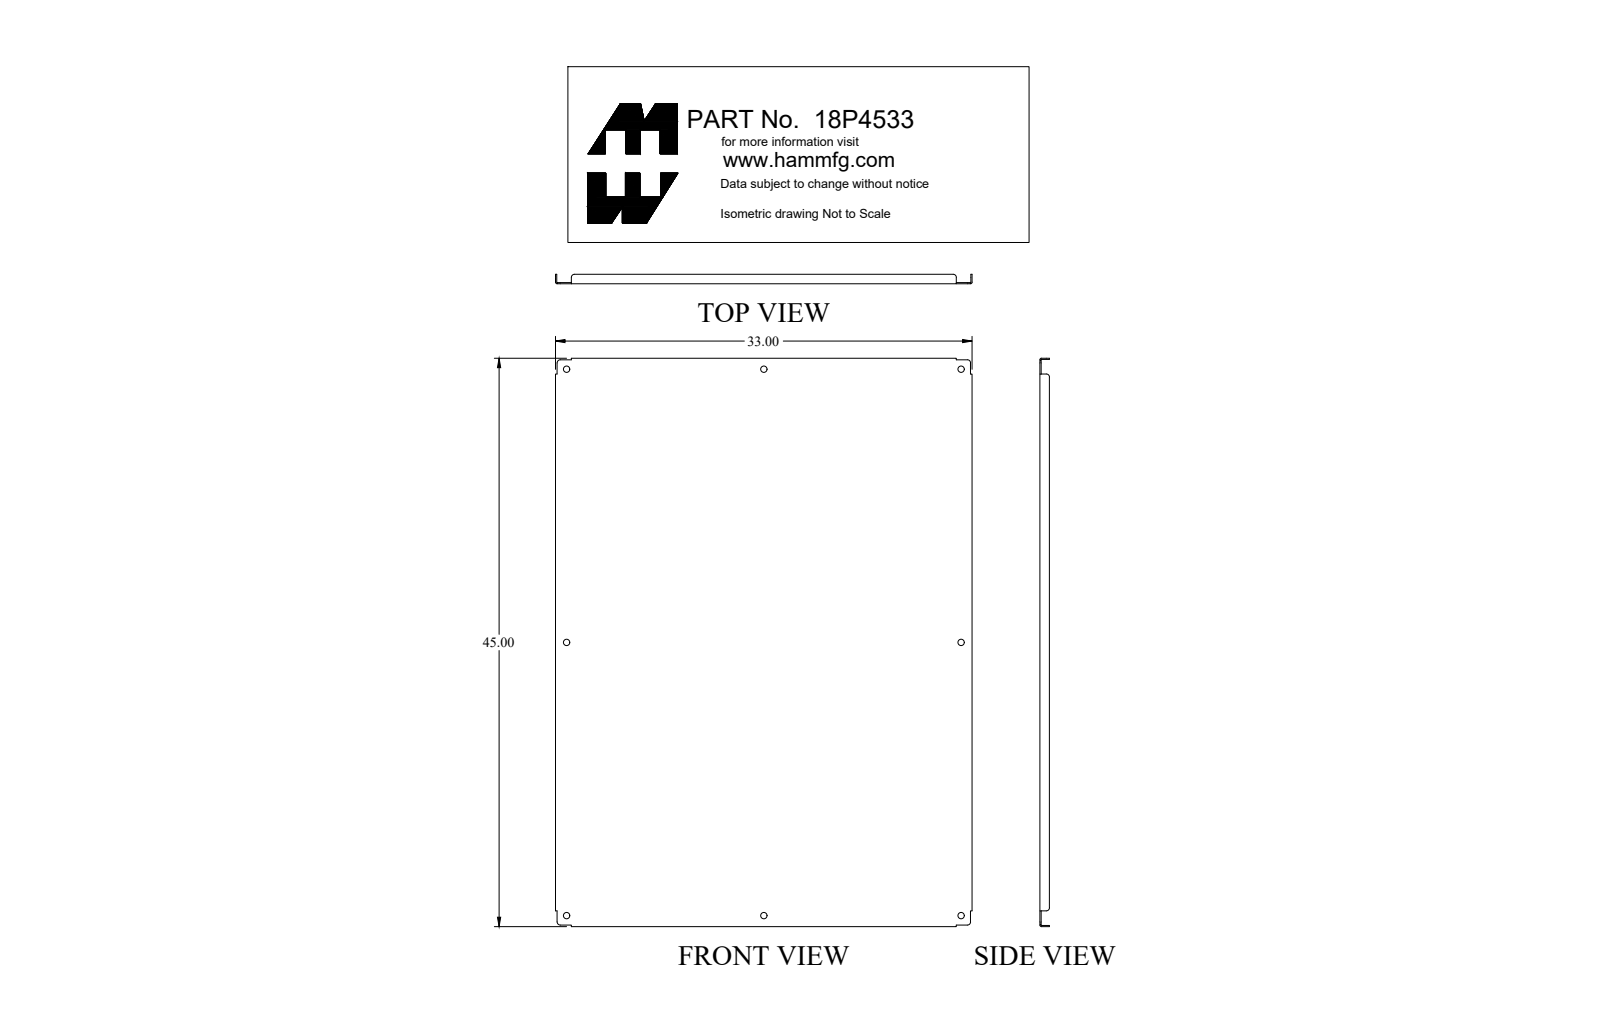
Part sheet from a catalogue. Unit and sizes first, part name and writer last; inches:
Units: inches
Overall size (bounding box): 45 × 33 × 0.75
Round holes (diameter × count): ⌀0.5 ×8
Partial cylindrical surfaces — rounded edges, fillets, slot ends (radius × count): R0.25 ×8, R0.03 ×4, R0.125 ×4
Main face-to-face distances: 0.095, 32.905, 44.905, 32.81, 33, 45, 44.81, 0.75, 0.655, 0.125
Hole centre spacings: 15.625, 21.625, 26.679, 38.003, 45.985, 31.25, 43.25, 53.358
Volume: 149.4 in³ · Surface area: 3 162 in²
Bodies: 1 solid, 66 faces (30 planar, 36 cylindrical, 0 other)
Part name (STEP PRODUCT): 18P4533_Default
STEP written by: SolidWorks 2018 (CONFIG_CONTROL_DESIGN)
